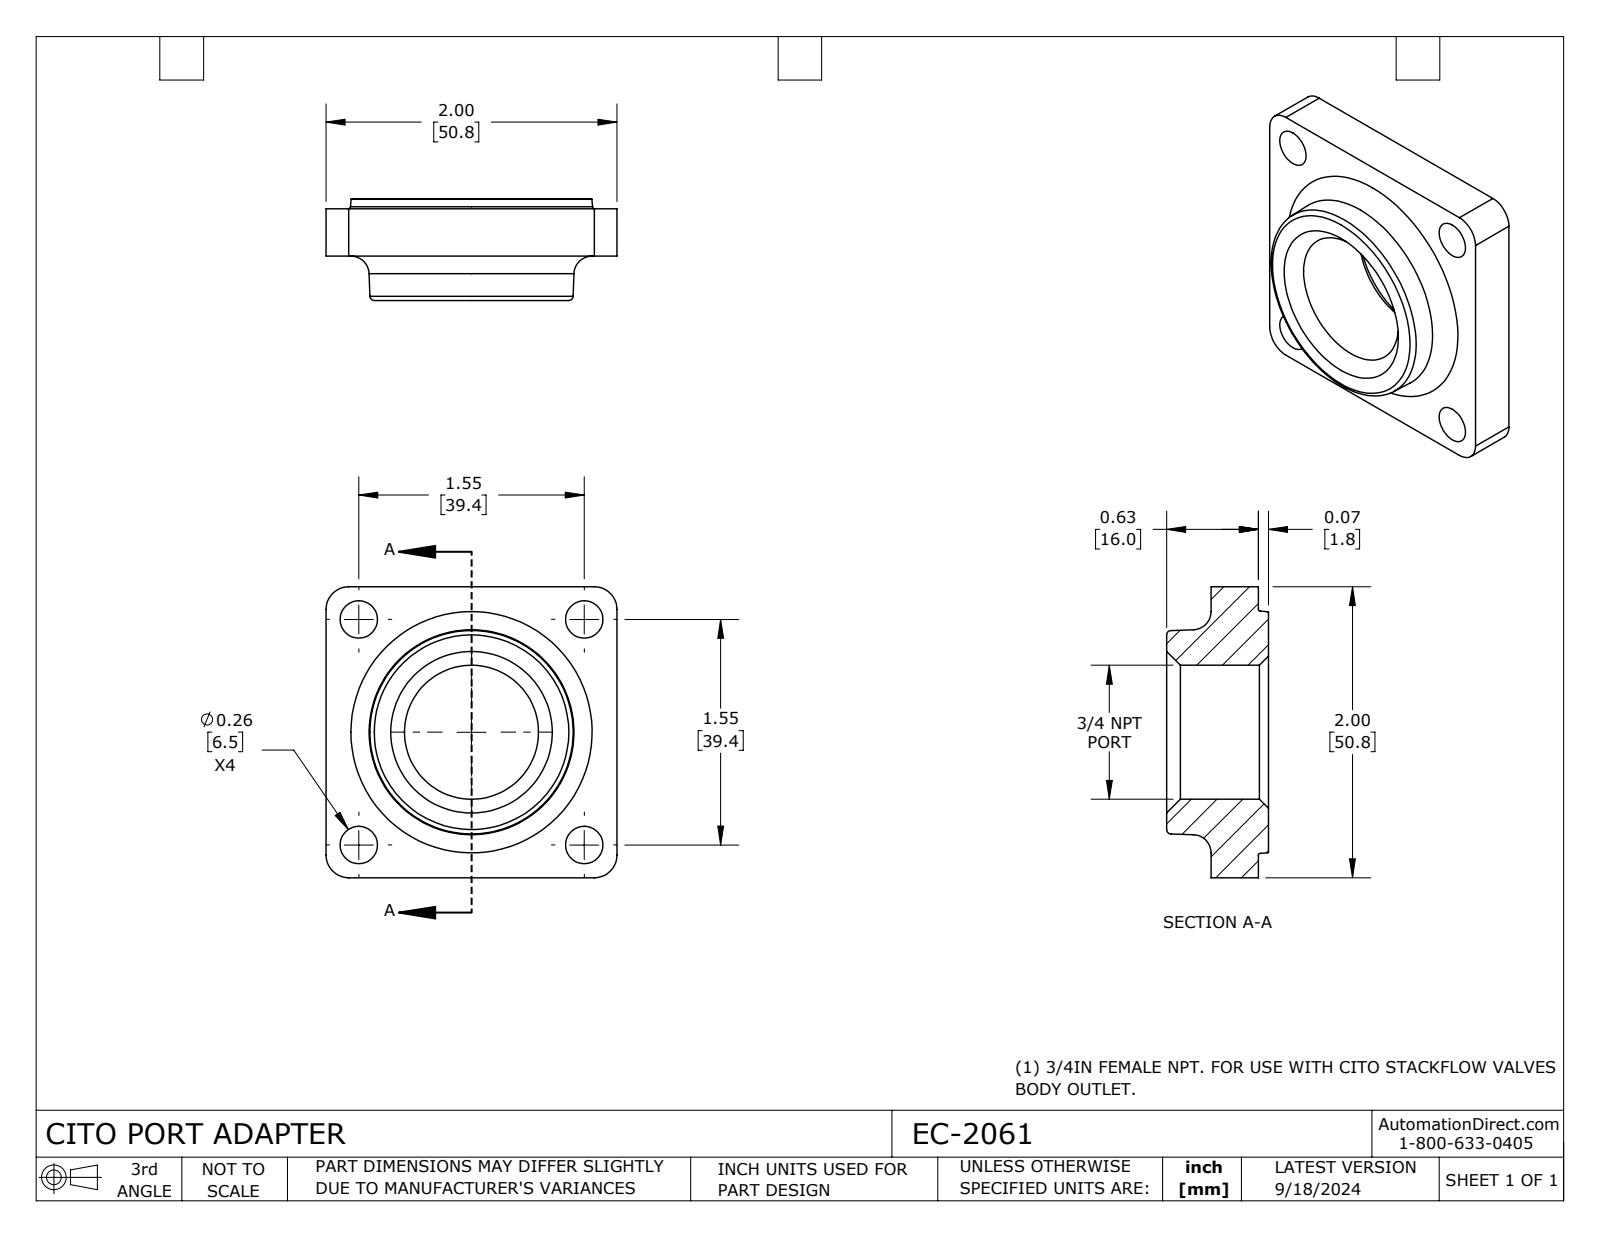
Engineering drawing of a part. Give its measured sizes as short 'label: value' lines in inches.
name: EC-2061
written by: SolidWorks 2023 (CONFIG_CONTROL_DESIGN)
unit: in
bodies: 1 solid, 38 faces (8 planar, 14 cylindrical, 16 other)
size: 2 × 2 × 0.7
volume: 1.379 in³; area: 12.88 in²
holes: 4× ⌀0.257, 1× ⌀0.921
rounds: 4× R0.156
face distances: 0.325, 0.395, 0.07, 2, 0.305, 0.63, 0.7
hole spacings: 1.096, 1.55, 2.191
